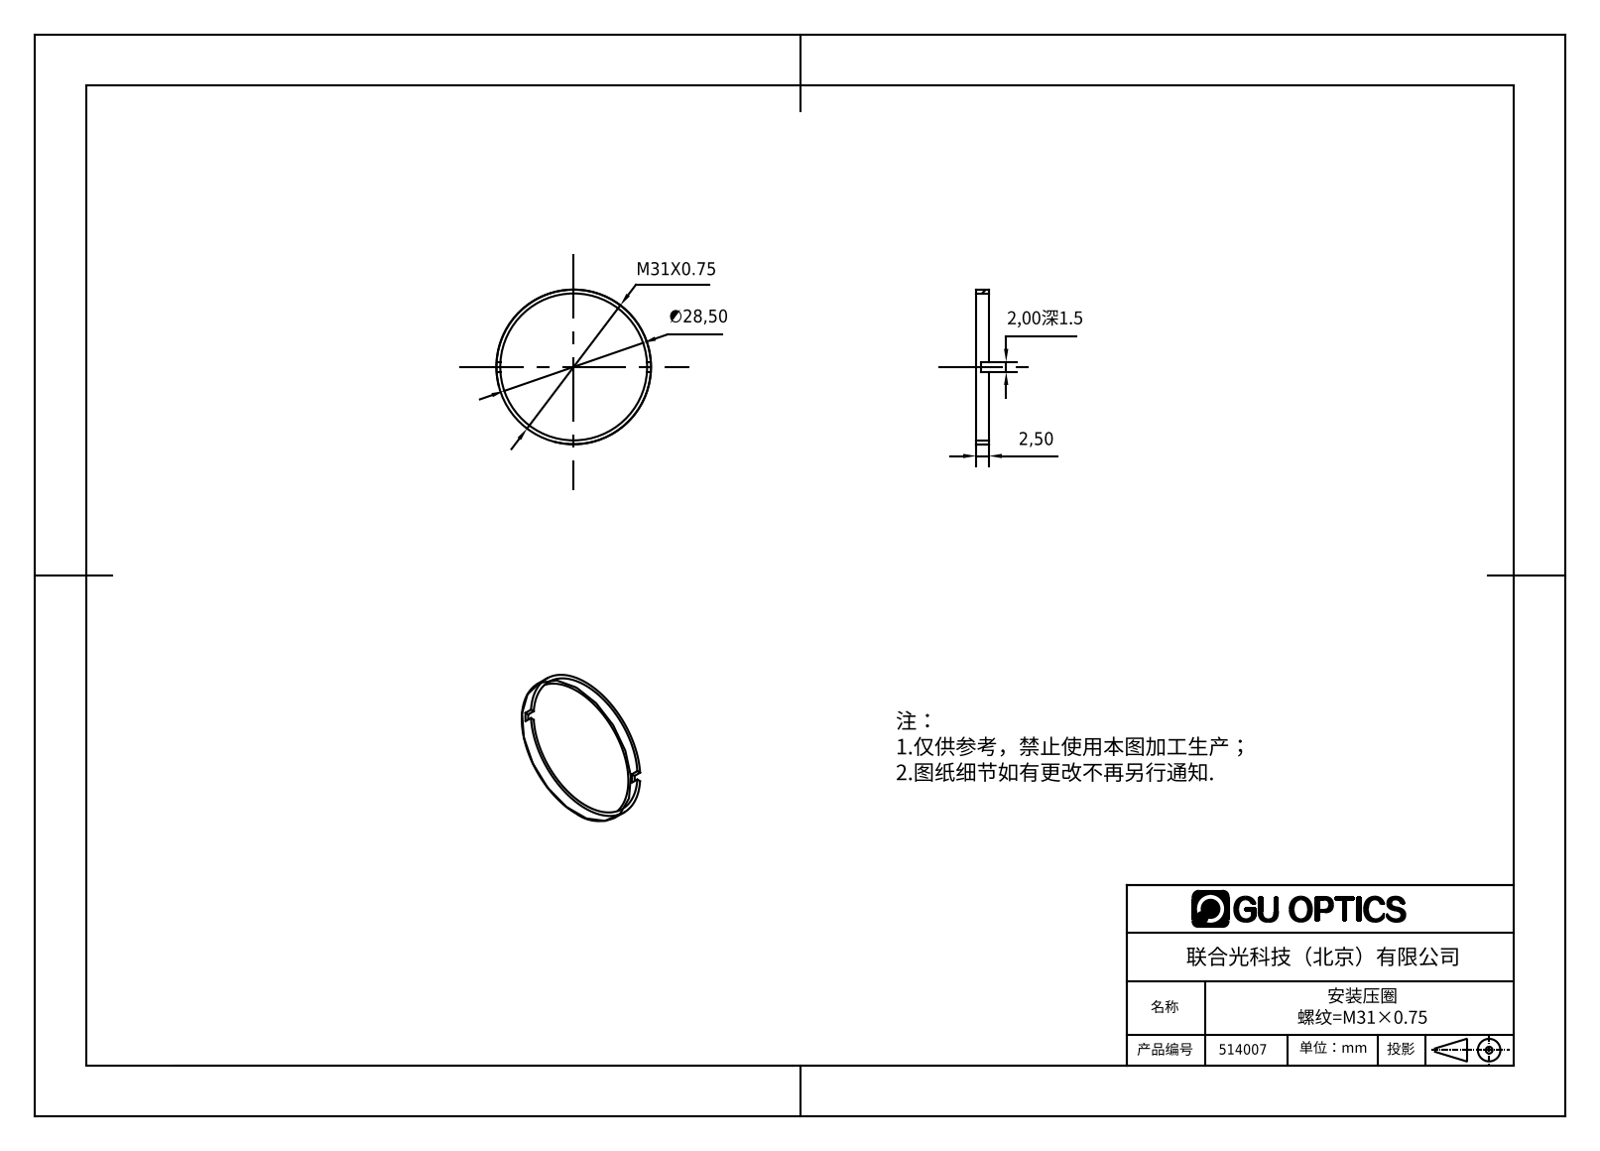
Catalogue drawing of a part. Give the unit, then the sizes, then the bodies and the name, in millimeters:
Units: millimetres
Overall size (bounding box): 30 × 30 × 2.5
Round holes (diameter × count): ⌀28.5 ×1
Round bosses / shafts (diameter × count): ⌀30 ×1
Main face-to-face distances: 2.5, 1, 1.5, 2
Volume: 168 mm³ · Surface area: 590 mm²
Bodies: 1 solid, 13 faces (9 planar, 4 cylindrical, 0 other)
Part name (STEP PRODUCT): 514007
STEP written by: SolidWorks 2016 (AUTOMOTIVE_DESIGN)
